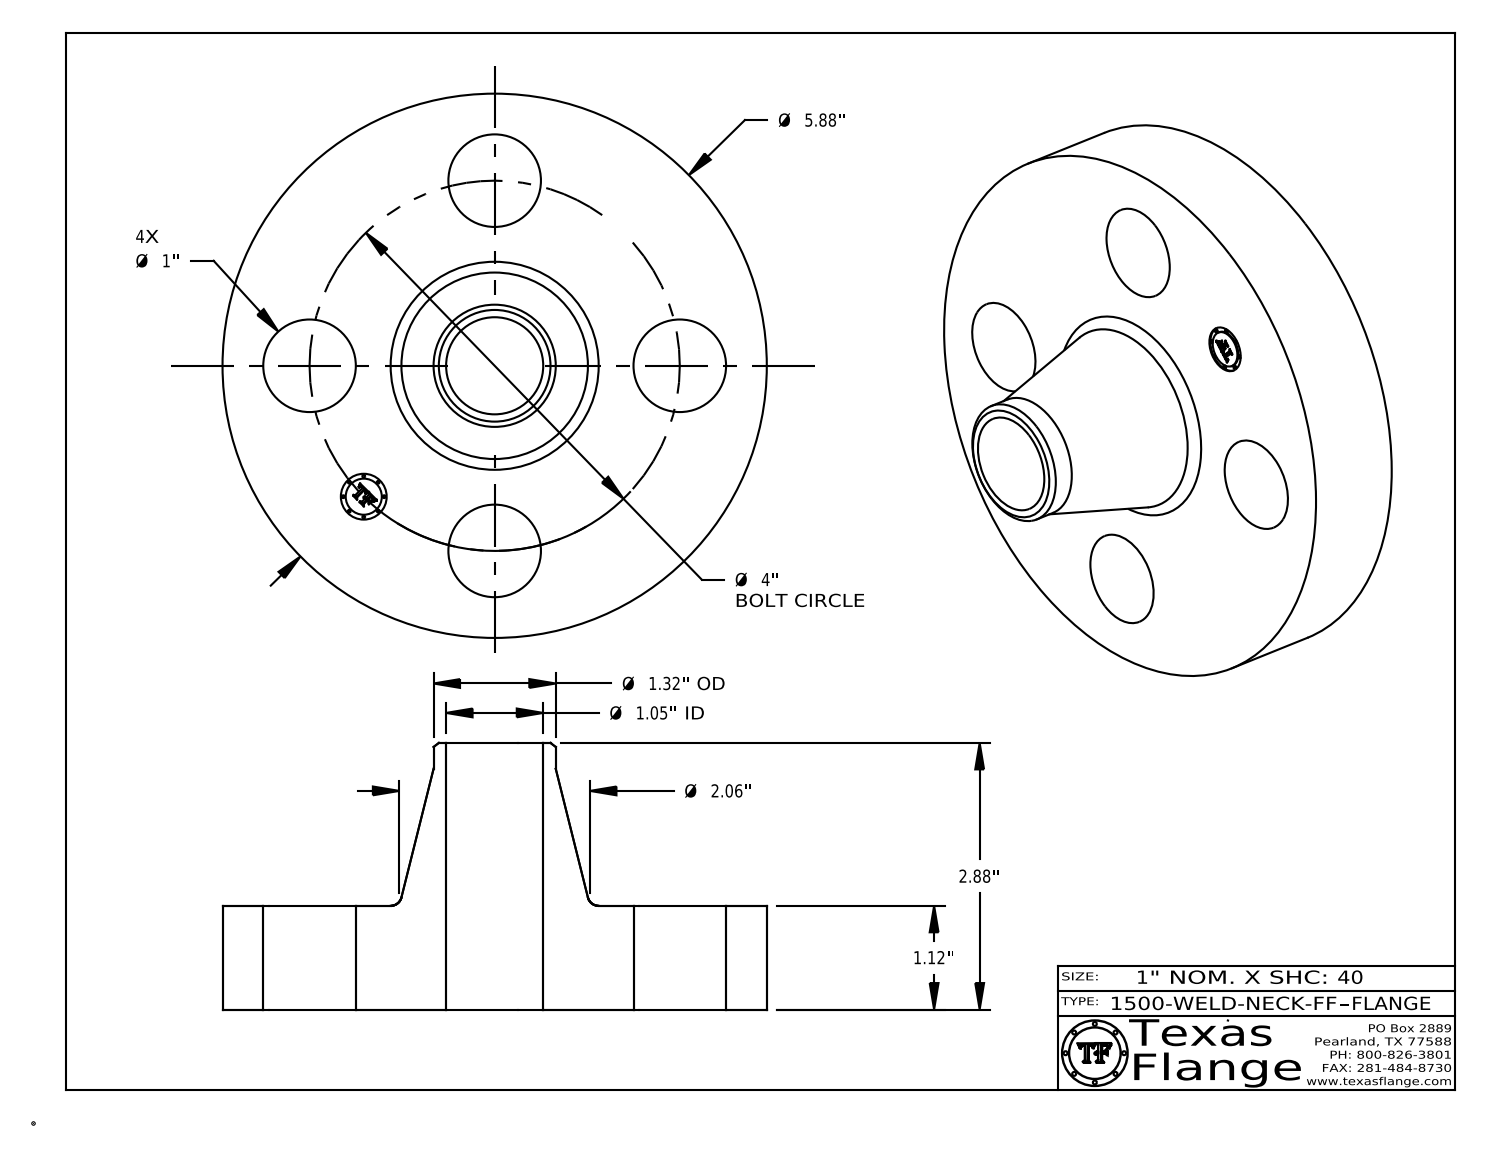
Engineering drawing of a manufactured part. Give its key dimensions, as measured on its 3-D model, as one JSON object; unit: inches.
{"part_name": "1500-WELD-NECK-FF", "step_written_by": "CATIA V5 STEP AP214 (AUTOMOTIVE_DESIGN)", "units": "inches", "bodies": {"solids": 1, "faces": 408, "planar": 368, "cylindrical": 34, "other": 6}, "overall_size": [5.88, 5.88, 2.88], "volume_in3": 28.17, "surface_area_in2": 97.64, "round_holes": [[1, 4], [0.495, 1], [1.049, 1]], "round_bosses_or_shafts": [[0.03, 8], [5.88, 1], [1.32, 1], [0.39, 1]], "face_to_face_distances": [1.12, 2.88, 1.76, 0.015, 1.105, 1.775, 0.148, 0.145, 0.027, 0.096], "hole_center_spacings": [2, 2.828, 1.531, 3.695, 4]}
